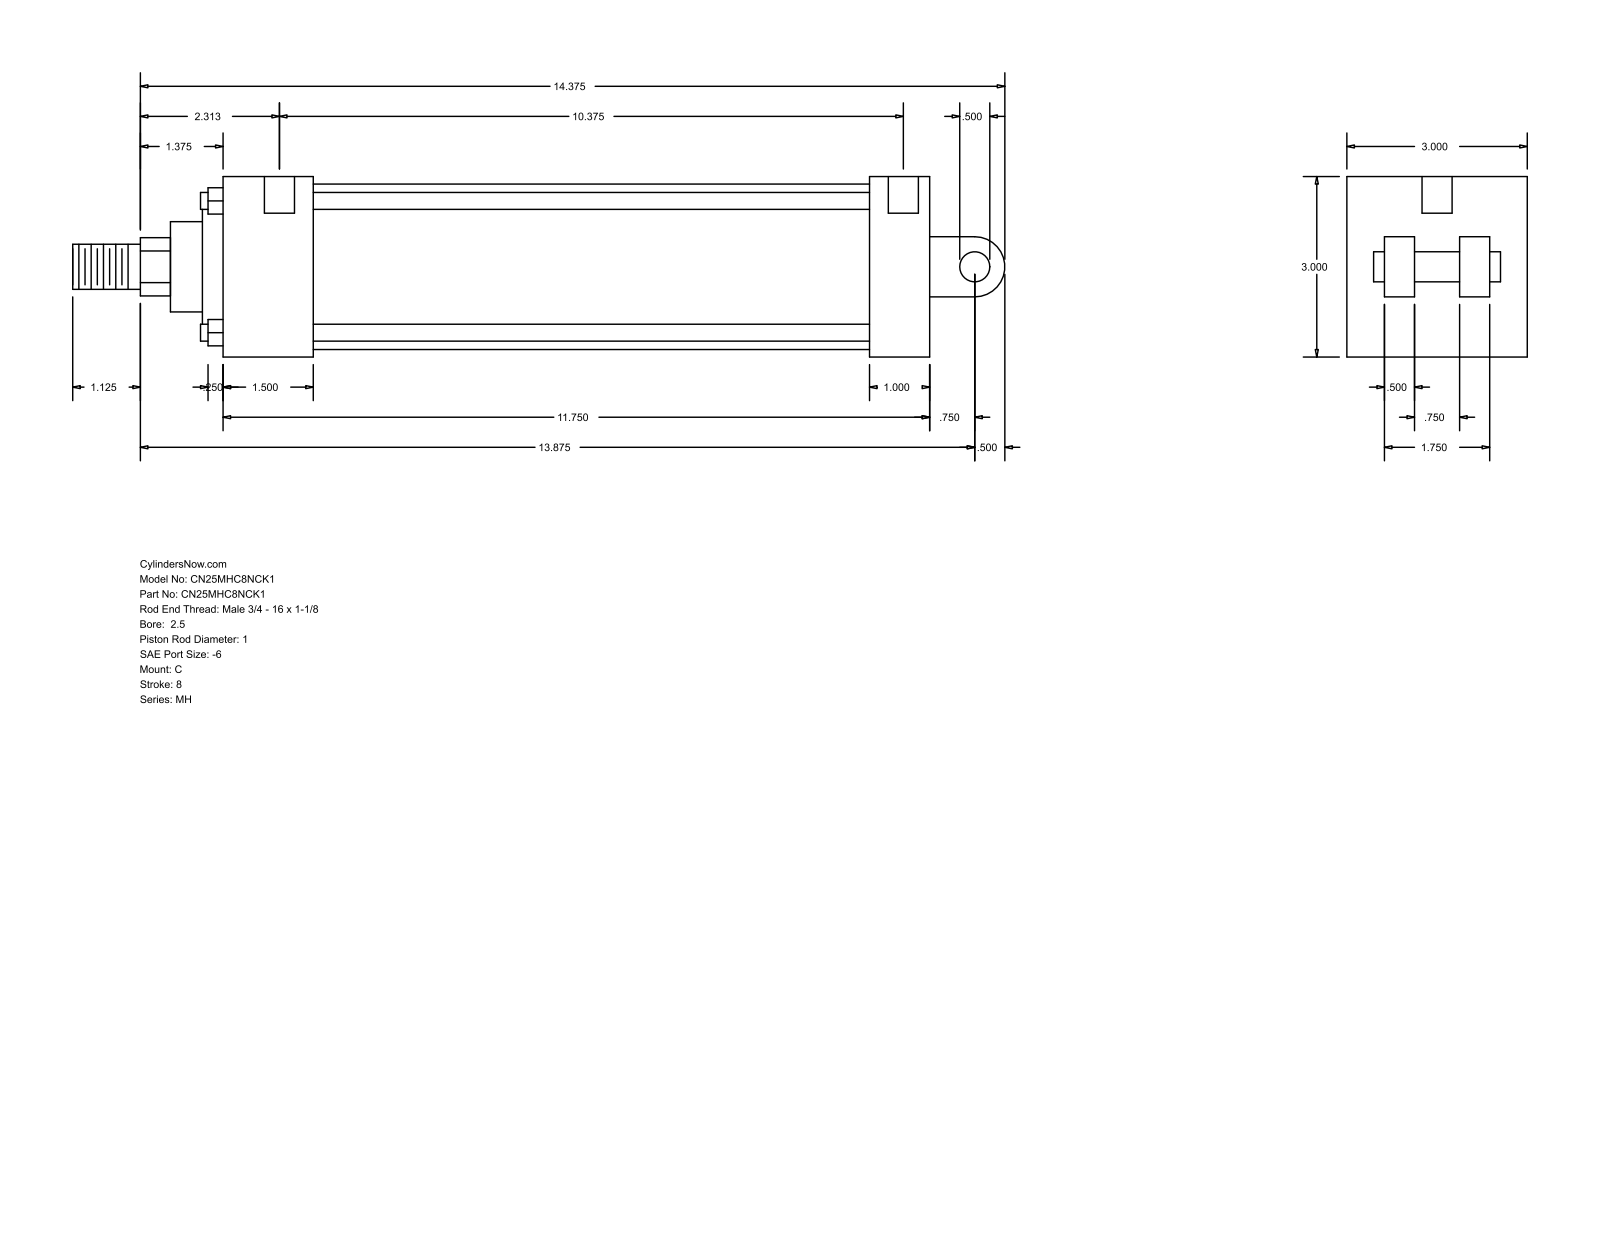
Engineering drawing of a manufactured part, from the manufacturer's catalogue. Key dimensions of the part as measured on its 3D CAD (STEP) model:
Part name (STEP PRODUCT): MH_C__0250_1
STEP written by: GSSL Pune (CONFIG_CONTROL_DESIGN)
Units: millimetres
Bodies: 0 solids, 101 faces (71 planar, 30 cylindrical, 0 other)
Overall size (bounding box): 393.7 × 76.2 × 76.2
Round holes (diameter × count): ⌀5.56 ×4, ⌀12.7 ×2
Round bosses / shafts (diameter × count): ⌀7.14 ×4, ⌀69.85 ×1, ⌀60.33 ×1, ⌀38.1 ×1, ⌀25.4 ×1, ⌀19.05 ×1, ⌀12.7 ×1
Partial cylindrical surfaces — rounded edges, fillets, slot ends (radius × count): R12.29 ×1, R12.7 ×1
Main face-to-face distances: 76.2, 25.4, 298.46, 60.33, 15.87, 273.06, 38.11, 234.95, 260.35, 12.7
Hole centre spacings: 271.46, 3.18, 4.76, 263.52, 266.7, 268.28
